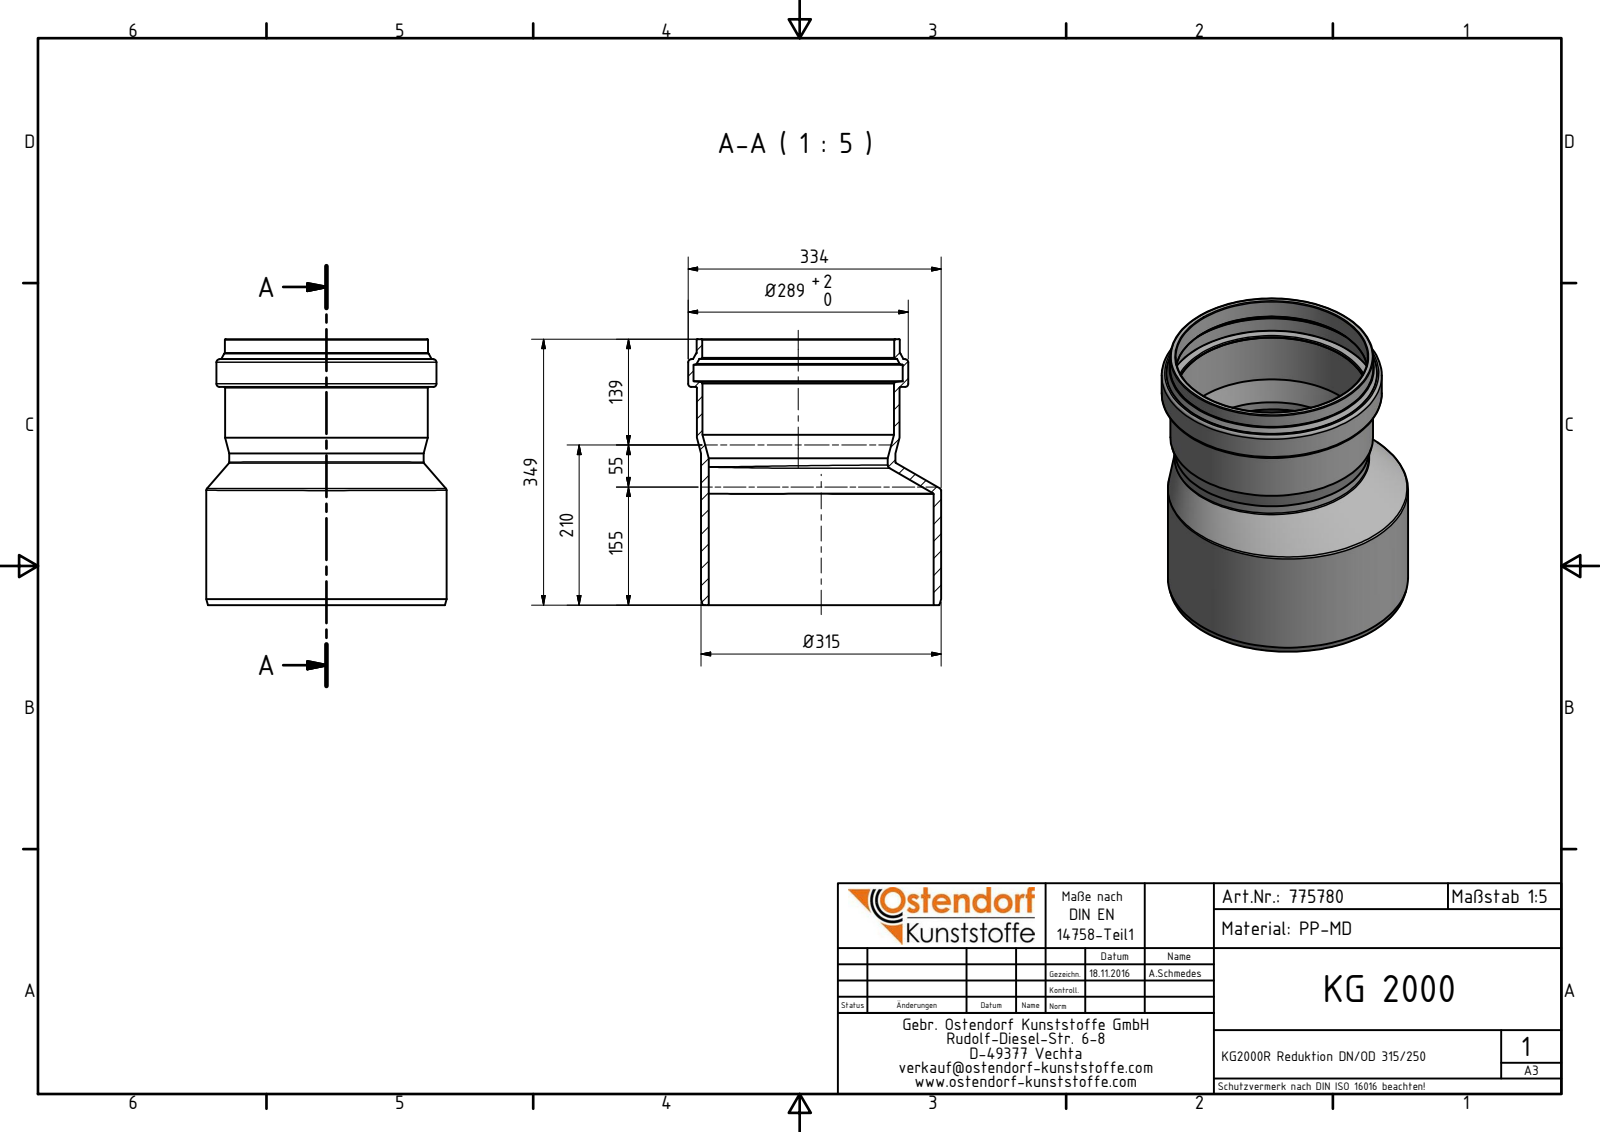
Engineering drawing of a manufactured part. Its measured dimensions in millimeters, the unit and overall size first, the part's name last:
Units: millimetres
Overall size (bounding box): 349 × 332.25 × 315.3
Round holes (diameter × count): ⌀235.1 ×1, ⌀251.7 ×1, ⌀252.1 ×1, ⌀274.6 ×1, ⌀295.3 ×1
Round bosses / shafts (diameter × count): ⌀315.3 ×1, ⌀289 ×1, ⌀266.5 ×1, ⌀266.1 ×1, ⌀255.1 ×1
Main face-to-face distances: 286.4, 349, 62.6, 322.7, 36.3, 26.3, 290.62, 4.22, 32.08, 58.38
Hole centre spacings: 30.1
Volume: 3 004 000 mm³ · Surface area: 682 778 mm²
Bodies: 1 solid, 44 faces (5 planar, 11 cylindrical, 28 other)
Part name (STEP PRODUCT): 775780 KG2000R Reduktion DN_OD 315_250
STEP written by: Autodesk Inventor 2016 (AUTOMOTIVE_DESIGN)
